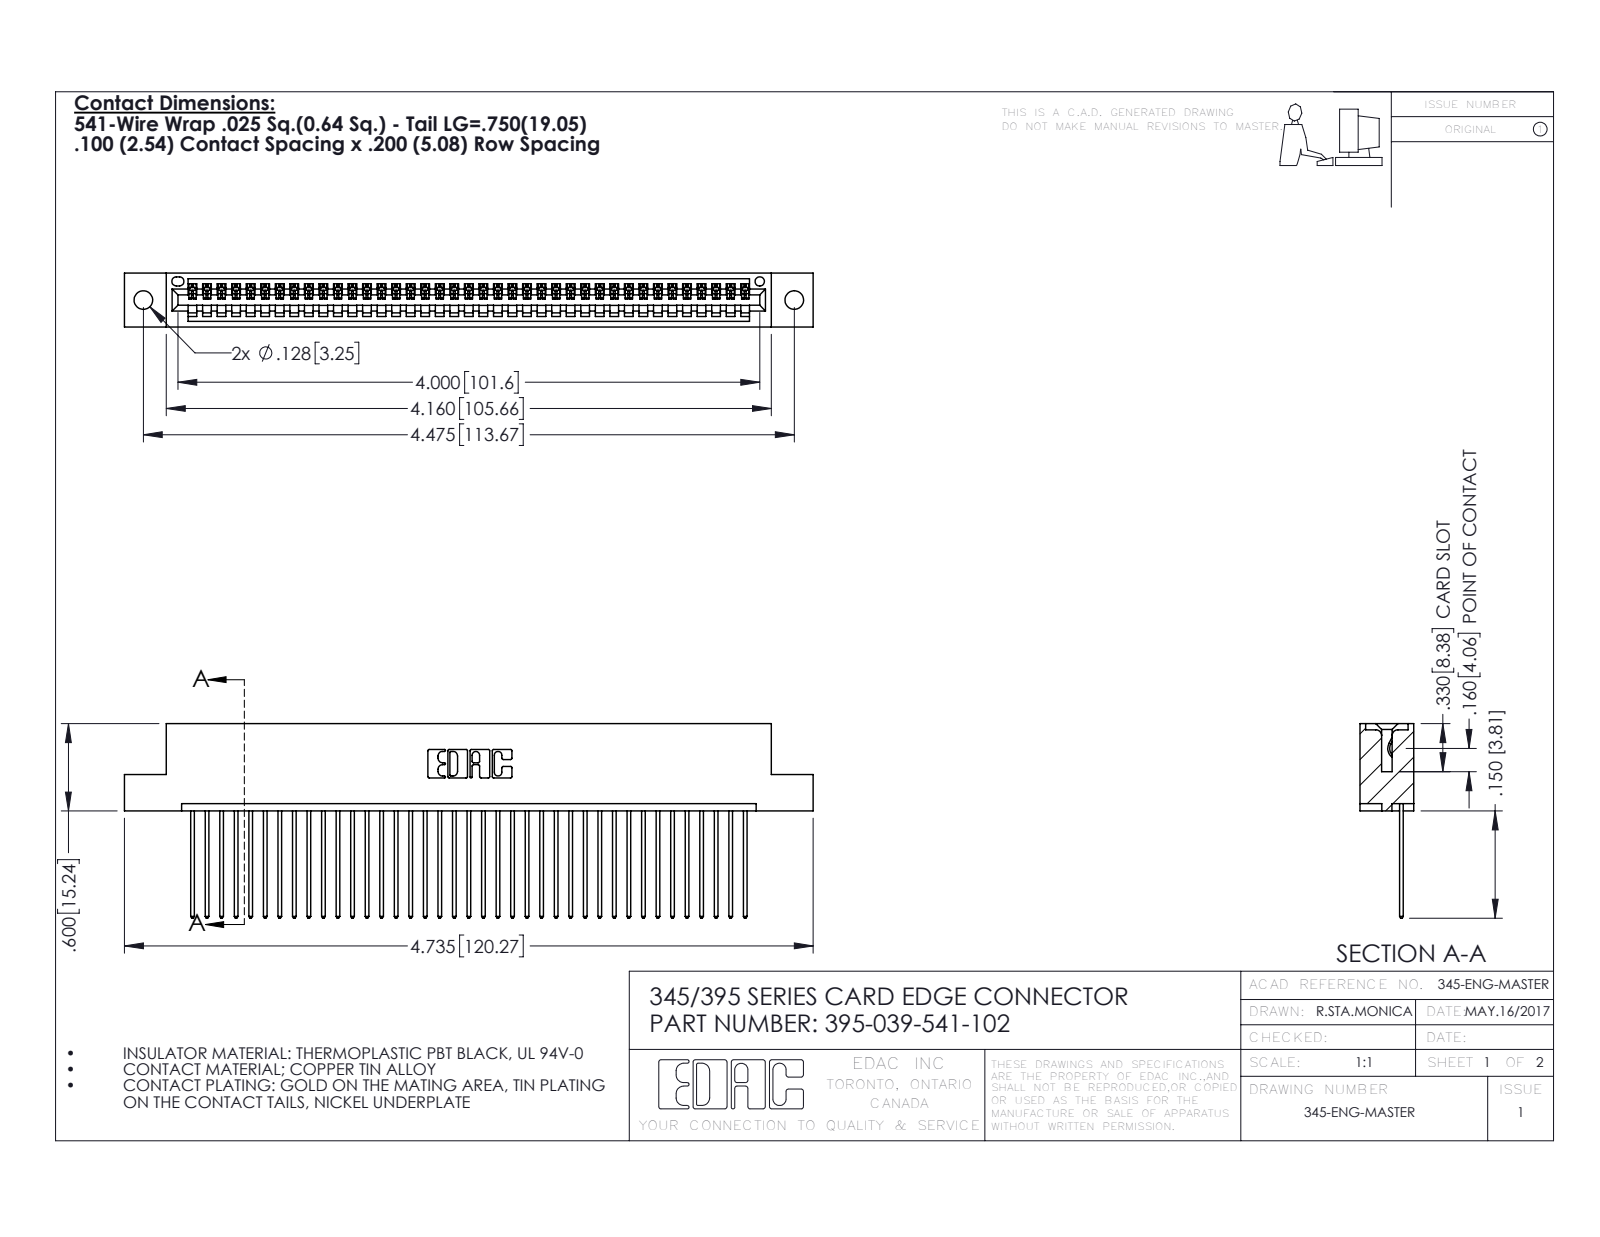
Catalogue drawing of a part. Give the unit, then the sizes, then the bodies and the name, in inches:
Units: inches
Overall size (bounding box): 4.735 × 1.337 × 0.37
Round holes (diameter × count): ⌀0.128 ×2, ⌀0.064 ×1
Partial cylindrical surfaces — rounded edges, fillets, slot ends (radius × count): R0.006 ×78, R0.01 ×78, R0.01 ×22, R0.007 ×6, R0.031 ×6, R0.026 ×3, R0.031 ×2, R0.04 ×2
Main face-to-face distances: 0.072, 0.298, 0.098, 0.272, 0.025, 0.37, 0.2, 0.225, 0.149, 0.072
Hole centre spacings: 0.27, 4.239, 4.475
Volume: 0.701 in³ · Surface area: 24.36 in²
Bodies: 40 solids, 2388 faces (1640 planar, 748 cylindrical, 0 other)
Part name (STEP PRODUCT): 345 Part_Flush Mounting Lugs - 0.128 Dia; 395-039-541-102; 345-292-001_345-293-141
STEP written by: SolidWorks 2016 (CONFIG_CONTROL_DESIGN)
